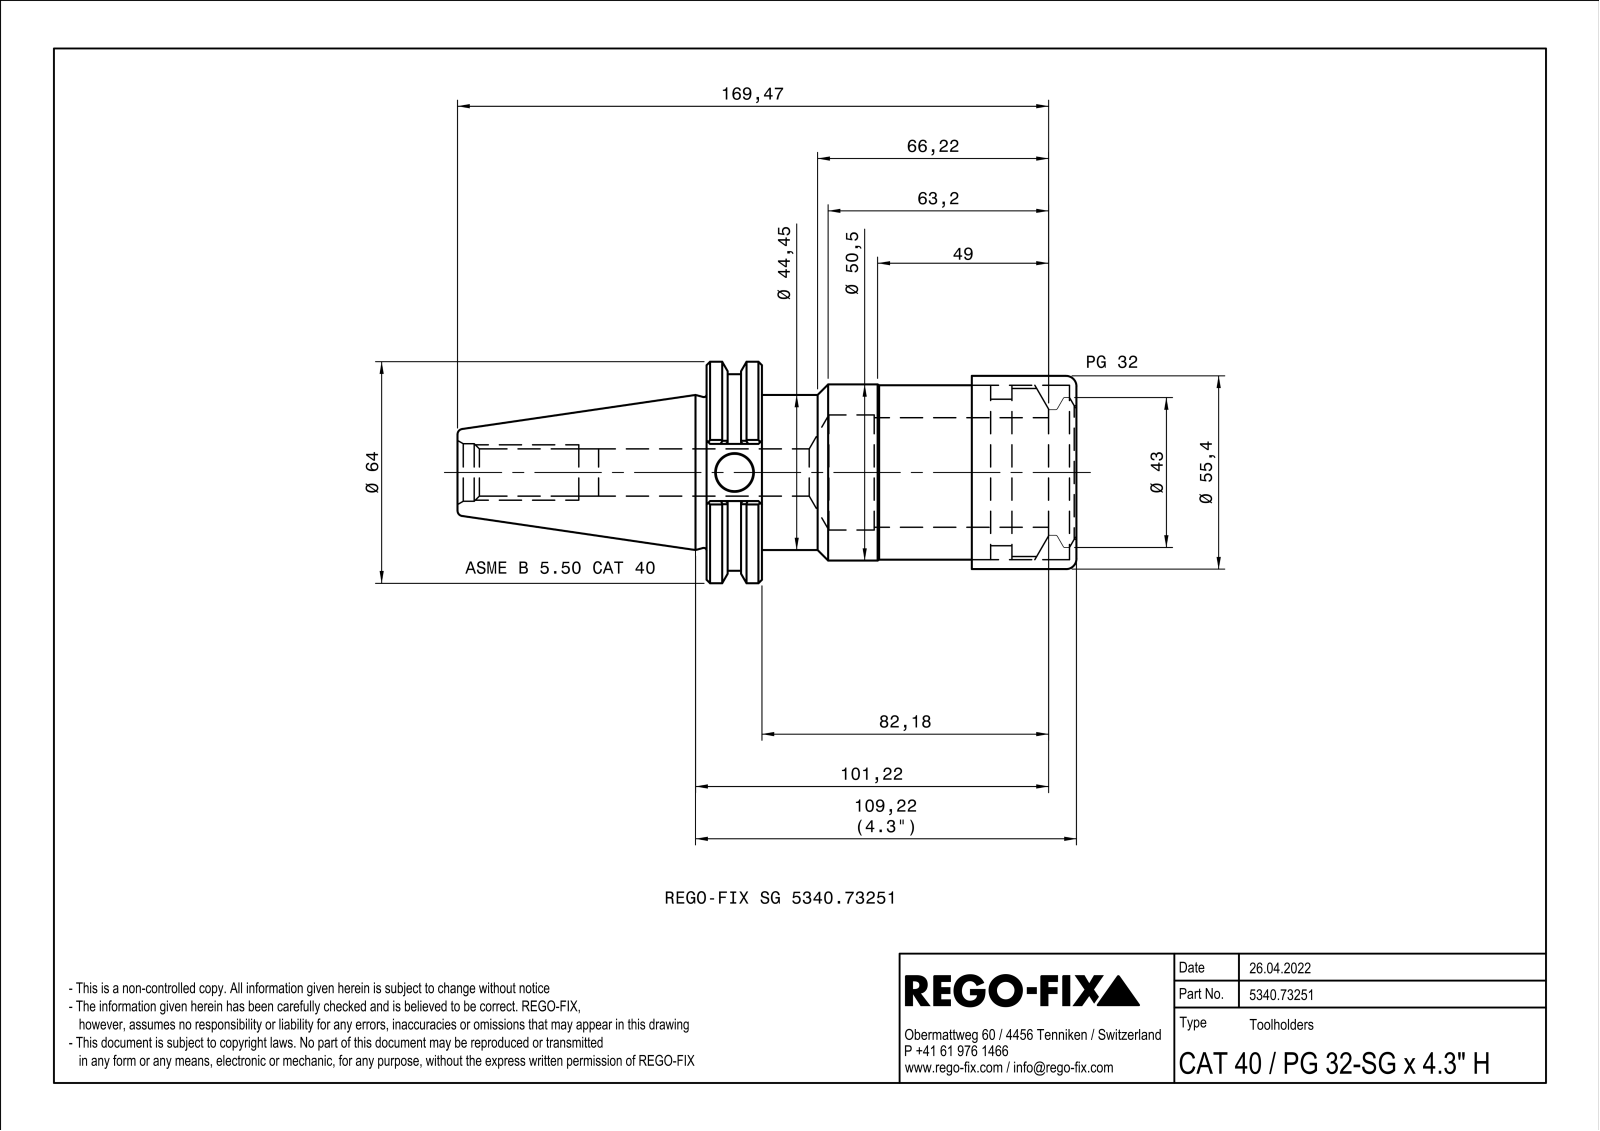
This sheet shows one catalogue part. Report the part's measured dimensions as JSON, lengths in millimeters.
{"part_name": "NOCUT", "step_written_by": "SIEMENS PLM Software Solid Edge ST10 (AUTOMOTIVE_DESIGN)", "units": "millimeters", "bodies": {"solids": 1, "faces": 108, "planar": 36, "cylindrical": 24, "other": 48}, "overall_size": [177.47, 63.5, 60.79], "volume_mm3": 207323, "surface_area_mm2": 50628, "round_holes": [[10.7, 1], [13.53, 1], [16.5, 1], [33, 1], [38.25, 1], [48.38, 1], [50.05, 1], [51, 1]], "round_bosses_or_shafts": [[63.5, 1], [56.36, 1], [55.4, 1], [55, 1], [50.5, 1], [50, 1], [44.45, 1], [42, 1]], "partial_cylinders_radius": [[0.5, 4]], "face_to_face_distances": [15.87, 90.18, 106.05, 24.6, 65.58, 81.45, 18.5, 6.1, 71.68, 87.55]}
